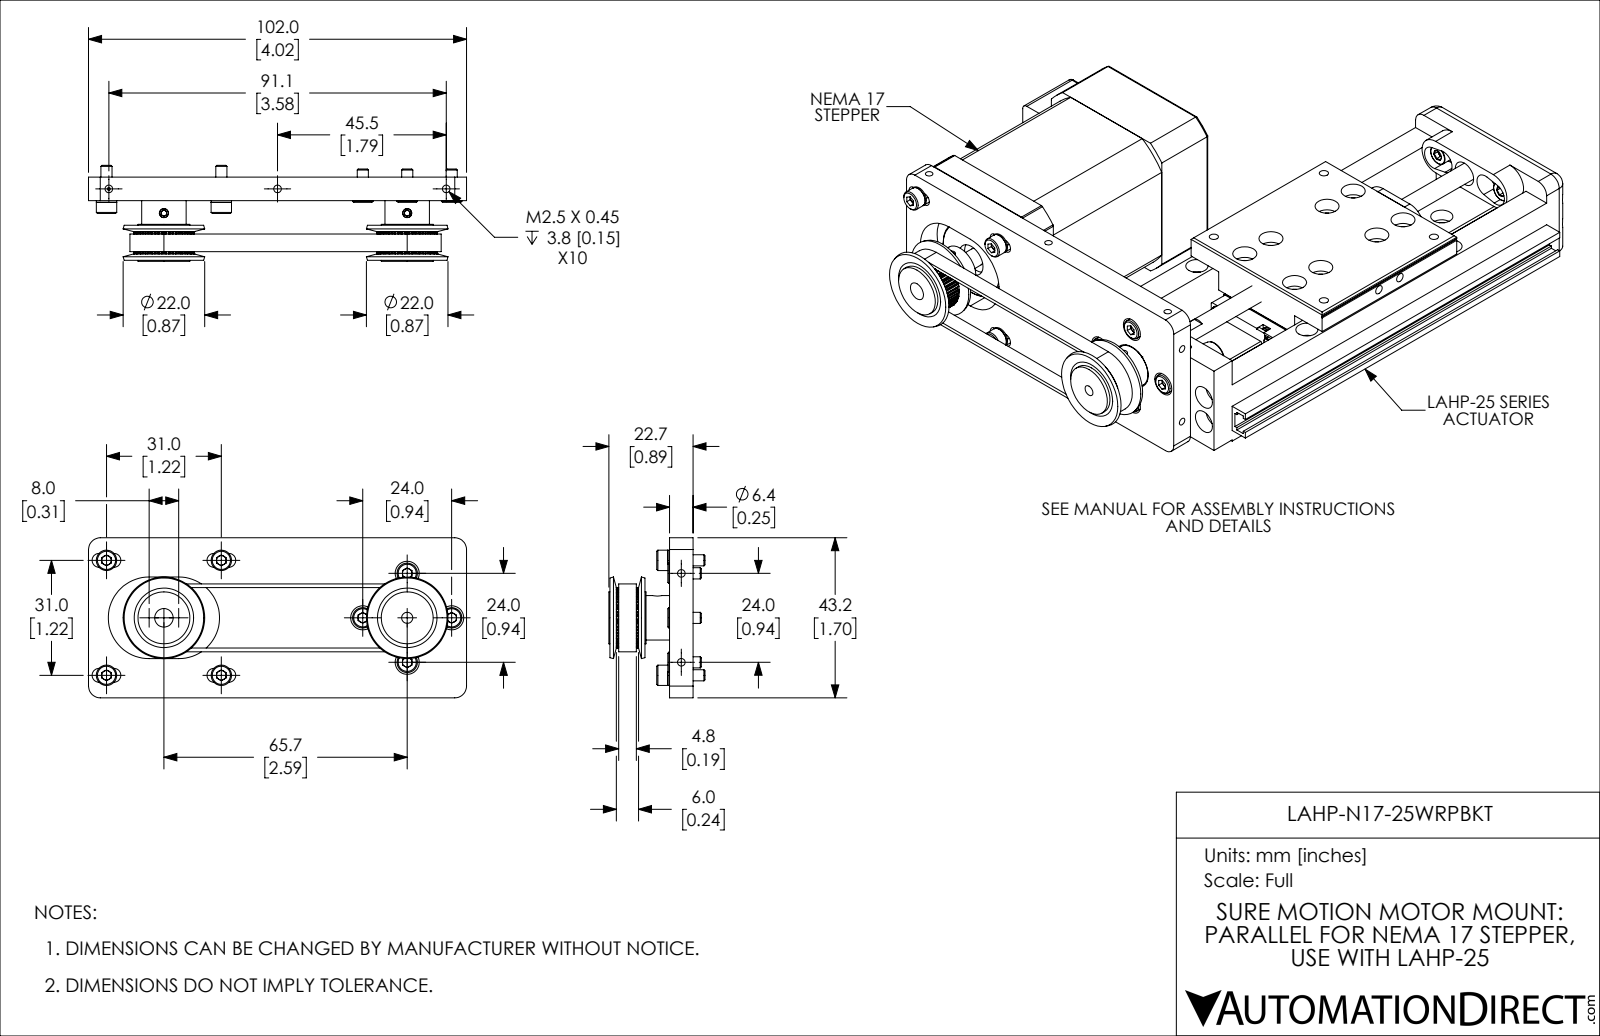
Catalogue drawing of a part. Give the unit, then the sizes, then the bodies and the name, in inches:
Units: inches
Overall size (bounding box): 4.016 × 1.7 × 1.02
Round holes (diameter × count): ⌀0.081 ×8, ⌀0.126 ×8, ⌀0.134 ×4, ⌀0.256 ×4, ⌀0.097 ×3, ⌀0.097 ×1, ⌀0.118 ×1, ⌀0.197 ×1, ⌀0.493 ×1
Round bosses / shafts (diameter × count): ⌀0.118 ×12, ⌀0.217 ×8, ⌀0.551 ×2, ⌀0.472 ×2
Partial cylindrical surfaces — rounded edges, fillets, slot ends (radius × count): R0.009 ×104, R0.012 ×104, R0.074 ×8, R0.125 ×4, R0.296 ×2, R0.321 ×2, R0.36 ×2, R0.434 ×2
Main face-to-face distances: 0.25, 0.039, 0.681, 1.7, 0.118, 1.171, 0.103, 1.211, 0.489, 1.171
Hole centre spacings: 1.793, 0.472, 0.668, 0.863, 1.22, 3.585, 0.639, 0.945
Volume: 1.809 in³ · Surface area: 30.17 in²
Bodies: 24 solids, 1089 faces (436 planar, 521 cylindrical, 132 other)
Part name (STEP PRODUCT): LAHP-N17-25WRPBKT
STEP written by: SolidWorks 2019 (CONFIG_CONTROL_DESIGN)
